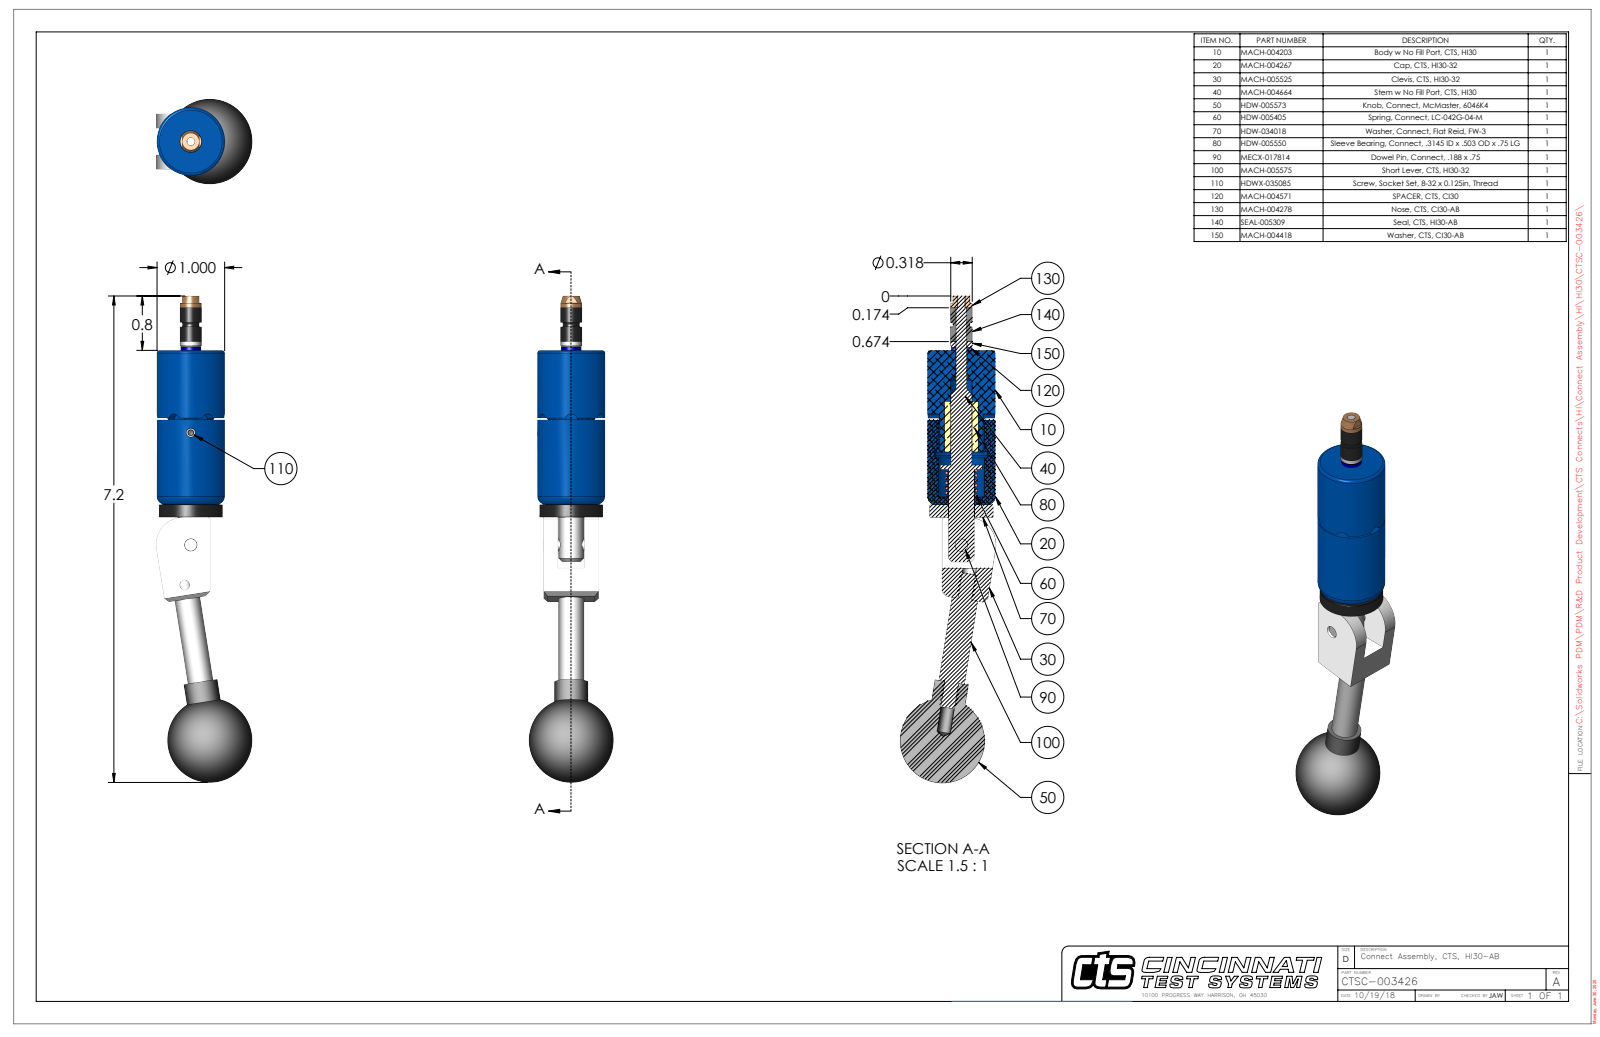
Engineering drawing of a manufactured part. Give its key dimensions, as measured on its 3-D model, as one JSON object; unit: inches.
{"part_name": "CTSC-003426", "step_written_by": "SolidWorks 2023 (AUTOMOTIVE_DESIGN)", "units": "inches", "bodies": {"solids": 11, "faces": 253, "planar": 96, "cylindrical": 99, "other": 58}, "overall_size": [7.193, 1.416, 1.25], "volume_in3": 3.715, "surface_area_in2": 29.19, "round_holes": [[0.201, 2], [0.113, 1], [0.136, 1], [0.15, 1], [0.155, 1], [0.161, 1], [0.164, 1], [0.189, 1], [0.385, 1], [0.392, 1]], "round_bosses_or_shafts": [[1, 1], [0.936, 1], [0.5, 1], [0.38, 1], [0.375, 1], [0.32, 1], [0.317, 1], [0.3, 1]], "partial_cylinders_radius": [[0.093, 6], [0.015, 1], [0.344, 1], [0.4, 1], [0.472, 1]], "face_to_face_distances": [0.21, 0.602, 0.812, 0.187, 2.28, 2.467, 0.391, 1.026, 1.253, 1.441], "hole_center_spacings": [0.599, 1.658, 2.252]}
